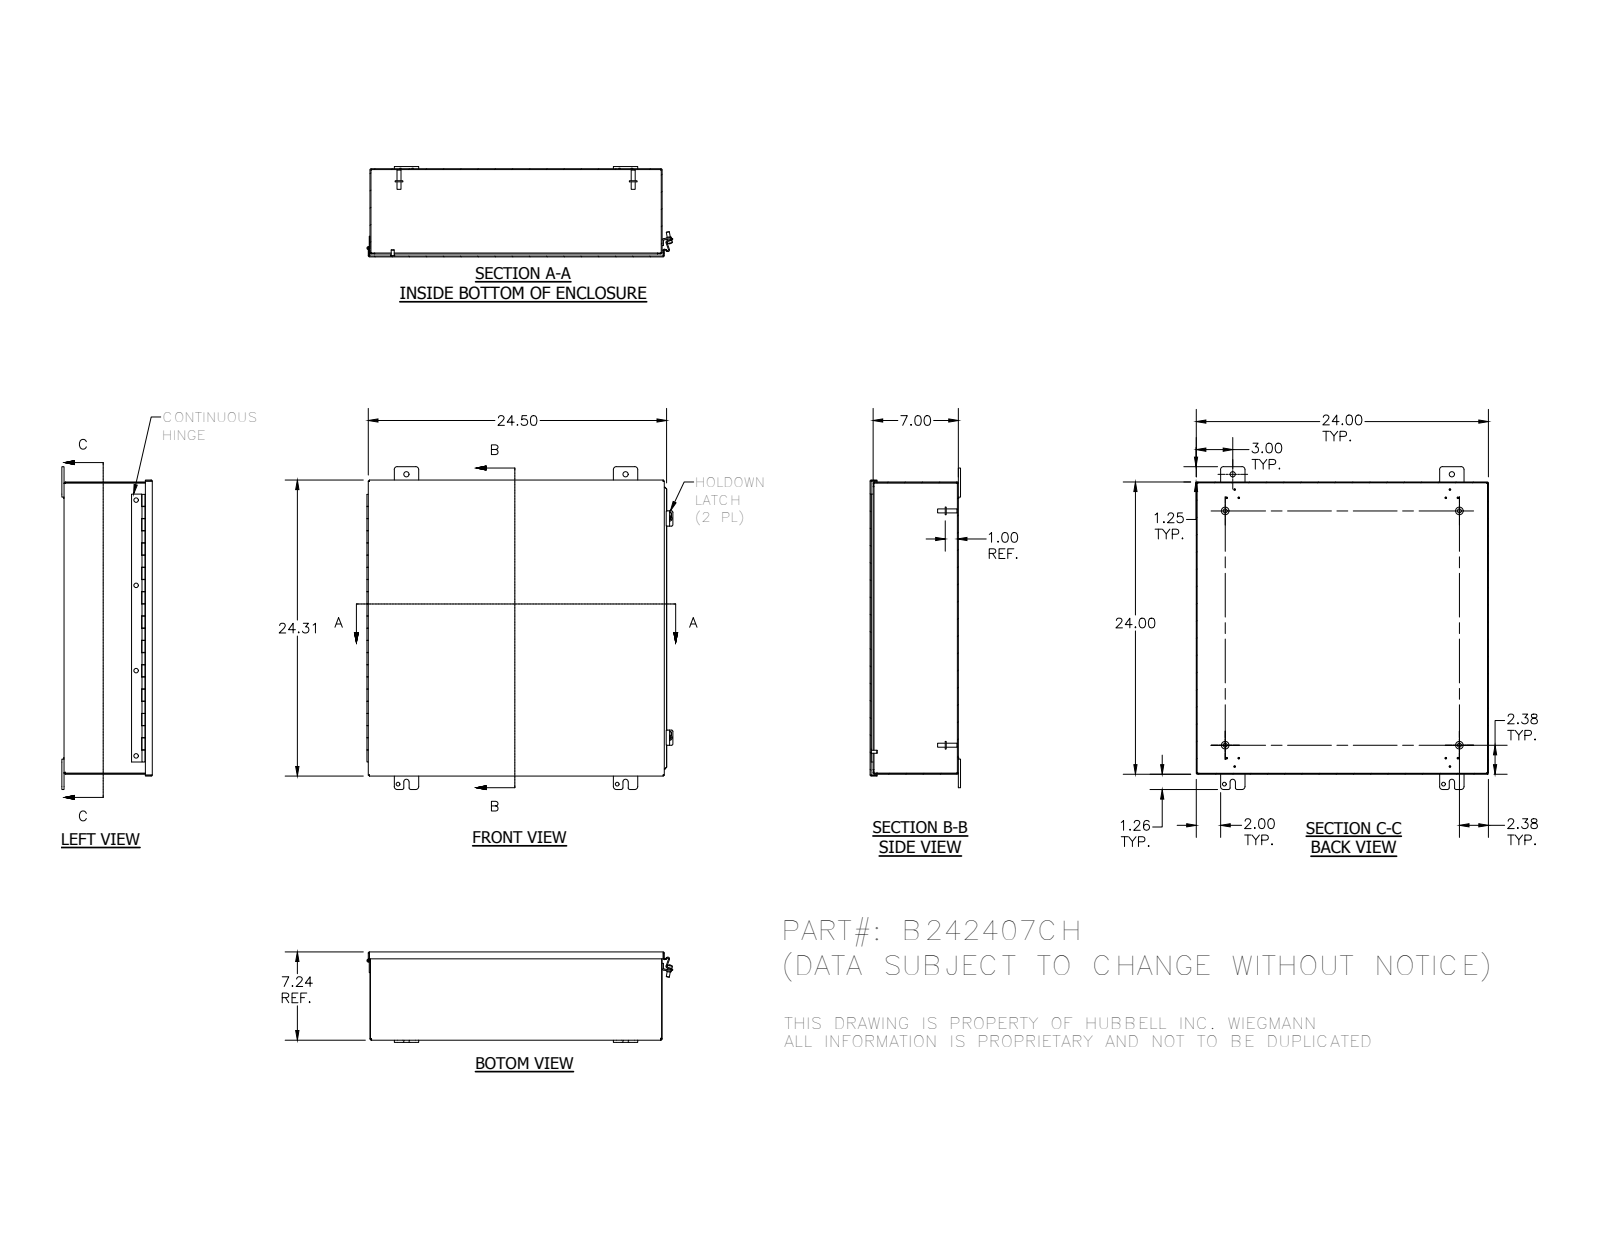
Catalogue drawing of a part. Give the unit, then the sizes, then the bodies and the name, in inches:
Units: inches
Overall size (bounding box): 26.505 × 25.136 × 7.423
Round holes (diameter × count): ⌀0.11 ×4, ⌀0.313 ×4, ⌀0.375 ×4, ⌀0.438 ×4, ⌀0.196 ×2, ⌀0.125 ×1, ⌀0.125 ×1
Round bosses / shafts (diameter × count): ⌀0.625 ×4, ⌀0.33 ×4, ⌀0.25 ×4, ⌀0.41 ×2, ⌀0.344 ×2, ⌀0.337 ×1, ⌀0.12 ×1
Partial cylindrical surfaces — rounded edges, fillets, slot ends (radius × count): R0.125 ×16, R0.25 ×16, R0.031 ×8, R0.063 ×8, R0.07 ×8, R0.105 ×8, R0.016 ×5, R0.09 ×5
Main face-to-face distances: 0.074, 7.169, 23.926, 7.243, 7.095, 24, 23.852, 0.137, 24.063, 6.926
Hole centre spacings: 18, 30.004, 1.593, 7, 24.005, 0.75, 14, 17.372
Volume: 148.1 in³ · Surface area: 3 994 in²
Bodies: 20 solids, 649 faces (395 planar, 185 cylindrical, 69 other)
Part name (STEP PRODUCT): B242407CH; B242407CHBKP; B2424CHLID; H6010101 (+8 more)
STEP written by: Autodesk Inventor 2012 (AUTOMOTIVE_DESIGN)
